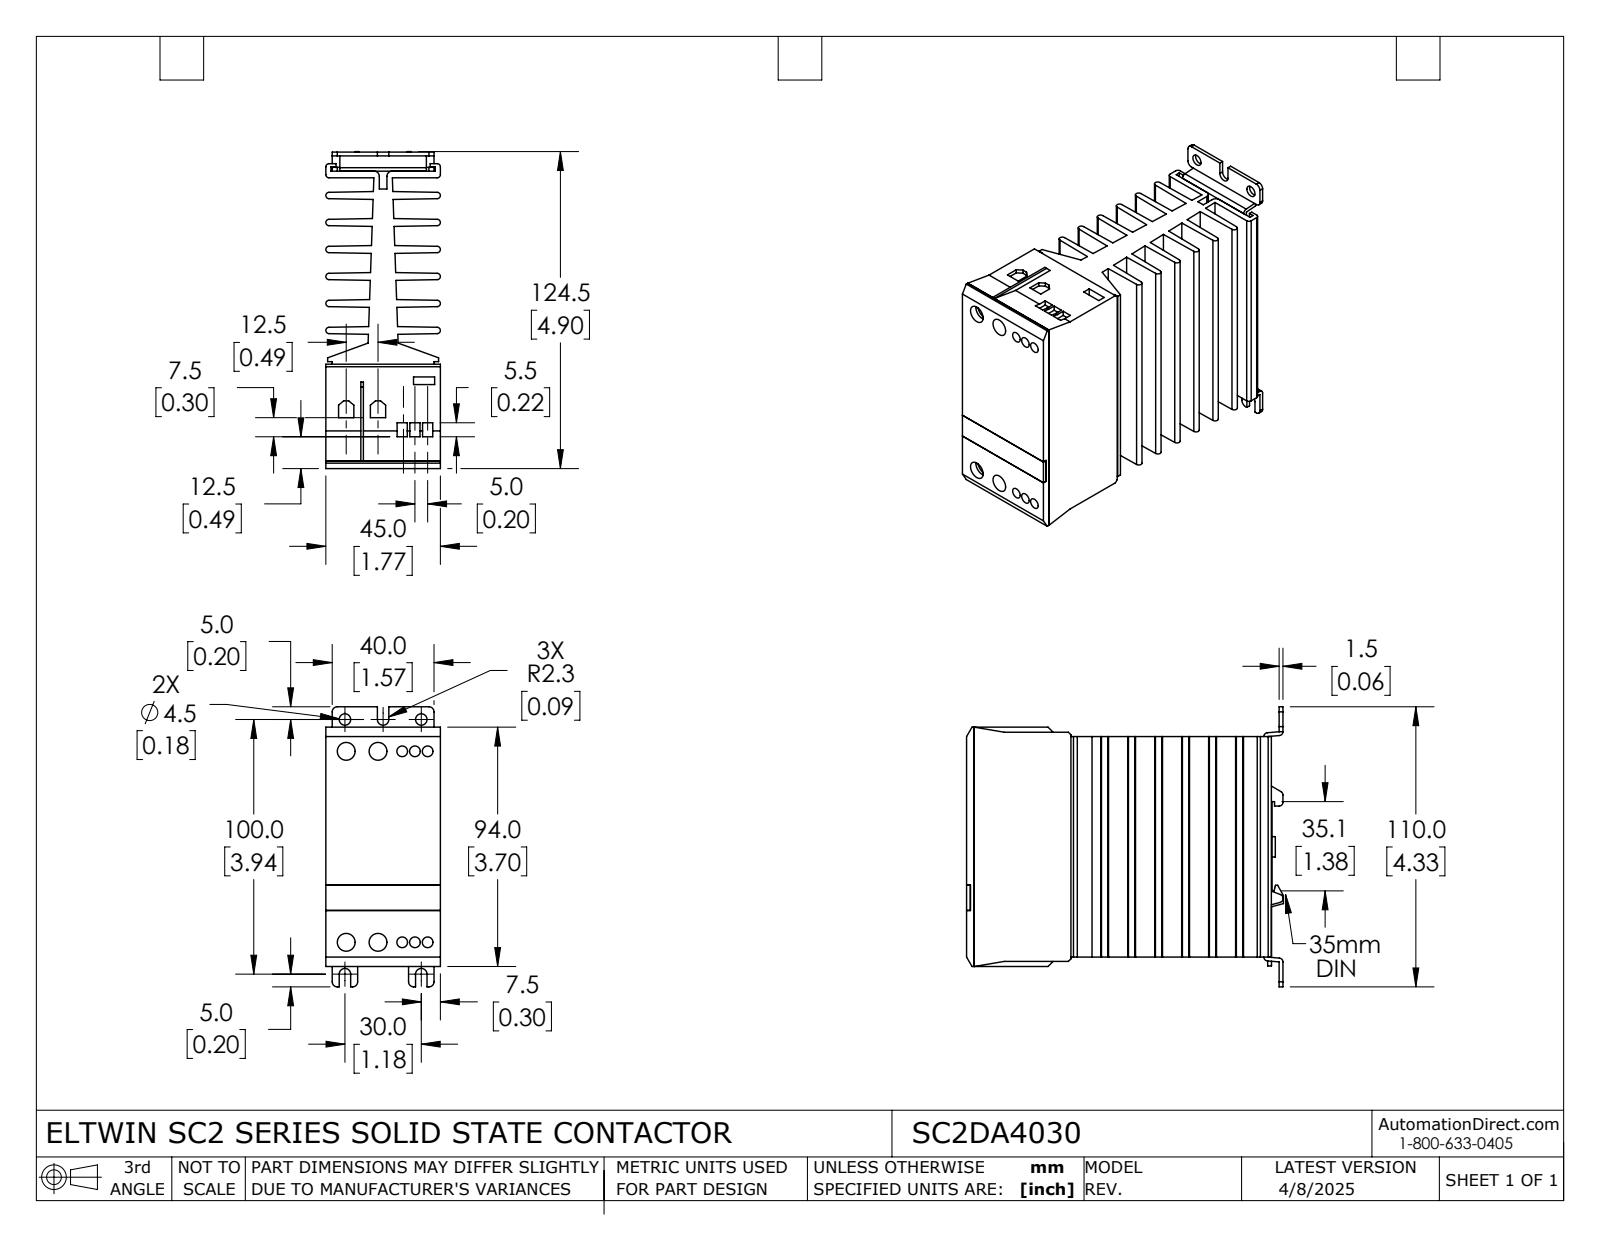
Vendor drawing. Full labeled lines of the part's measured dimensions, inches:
Part name (STEP PRODUCT): SC2DA4030
STEP written by: SolidWorks 2021 (AUTOMOTIVE_DESIGN)
Units: inches
Bodies: 7 solids, 391 faces (284 planar, 107 cylindrical, 0 other)
Overall size (bounding box): 4.902 × 4.331 × 1.772
Volume: 18.87 in³ · Surface area: 165.4 in²
Round holes (diameter × count): ⌀0.165 ×6, ⌀0.173 ×6, ⌀0.276 ×4, ⌀0.177 ×2, ⌀0.315 ×2
Round bosses / shafts (diameter × count): ⌀0.315 ×3
Partial cylindrical surfaces — rounded edges, fillets, slot ends (radius × count): R0.079 ×18, R0.049 ×16, R0.059 ×10, R0.051 ×4, R0.089 ×3
Main face-to-face distances: 0.417, 0.835, 0.127, 1.252, 0.29, 0.544, 0.707, 0.962, 1.669, 1.125
Hole centre spacings: 2.953, 0.197, 2.959, 0.374, 0.394, 0.492, 0.502, 0.571
